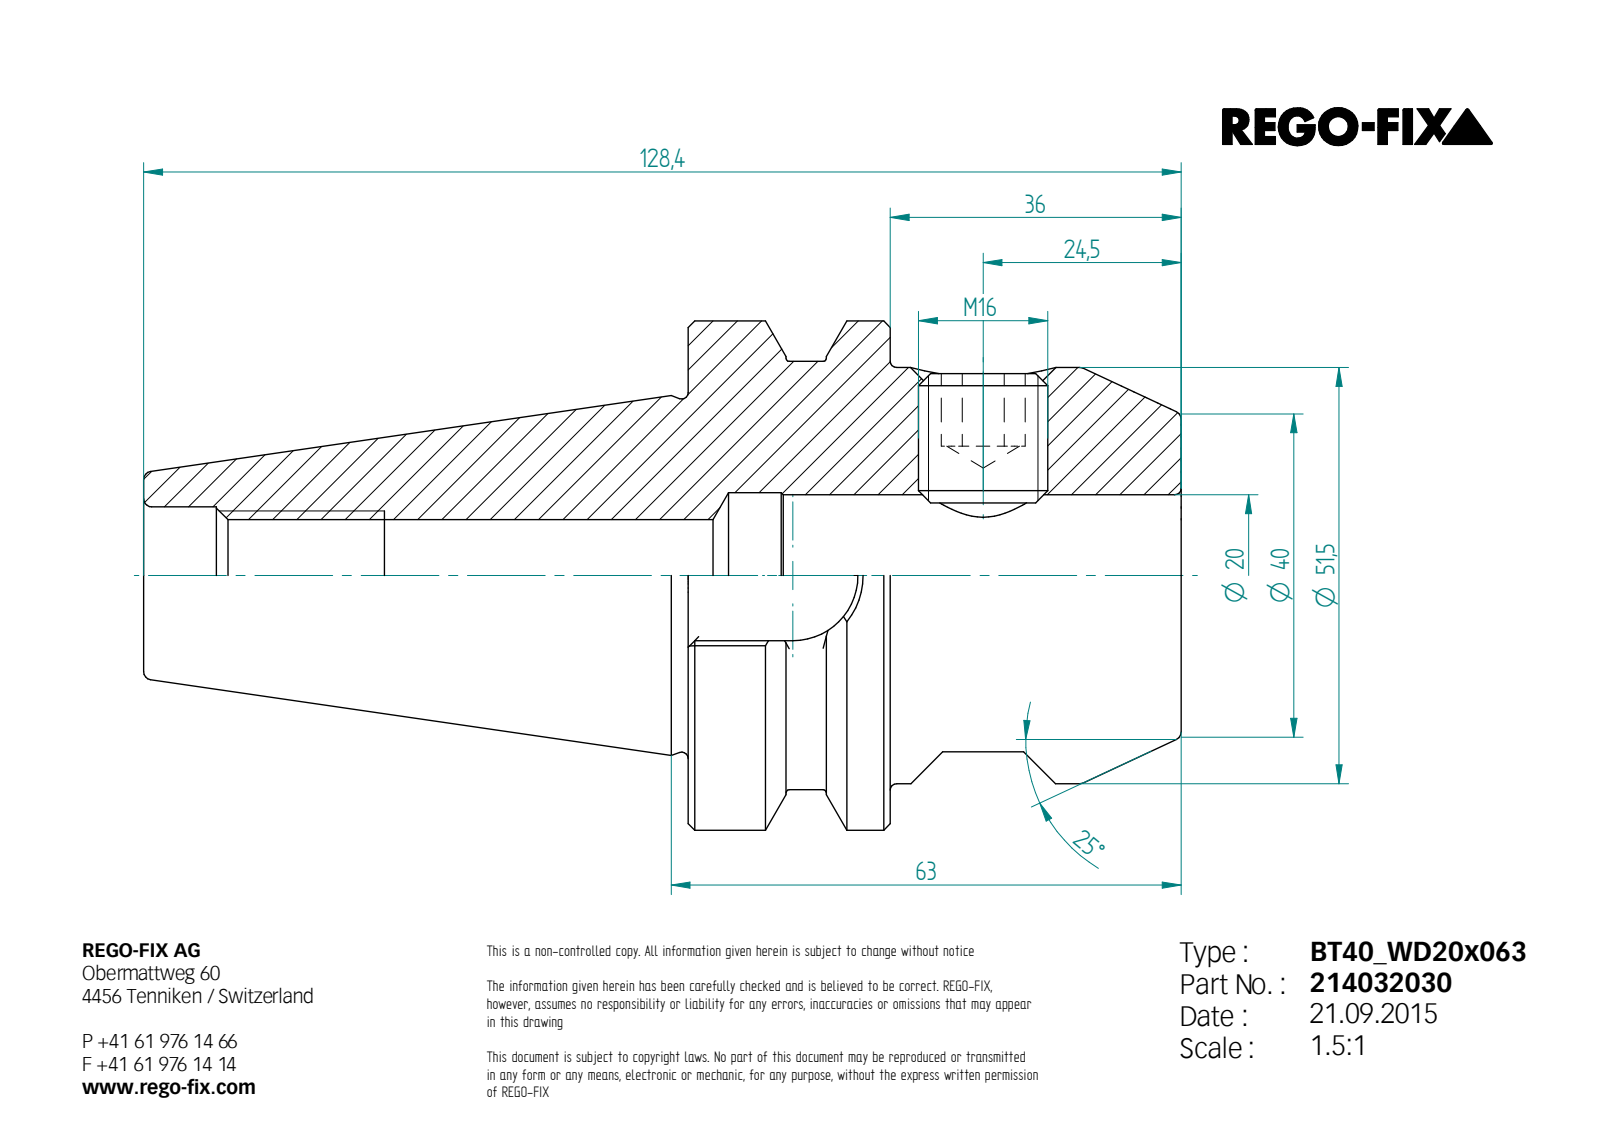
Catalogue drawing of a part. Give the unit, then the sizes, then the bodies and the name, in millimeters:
Units: millimetres
Overall size (bounding box): 128.4 × 63 × 63
Round holes (diameter × count): ⌀13.84 ×2, ⌀17 ×1, ⌀20 ×1, ⌀20.5 ×1
Round bosses / shafts (diameter × count): ⌀63 ×1, ⌀53 ×1, ⌀51.5 ×1, ⌀16 ×1
Partial cylindrical surfaces — rounded edges, fillets, slot ends (radius × count): R0.5 ×4, R8.05 ×1
Main face-to-face distances: 61, 25, 36, 45.1, 67.4, 92.4, 128.4, 9, 13.75, 29.85
Volume: 173 687 mm³ · Surface area: 31 571 mm²
Bodies: 2 solids, 104 faces (53 planar, 19 cylindrical, 32 other)
STEP written by: Unknown (AUTOMOTIVE_DESIGN)
